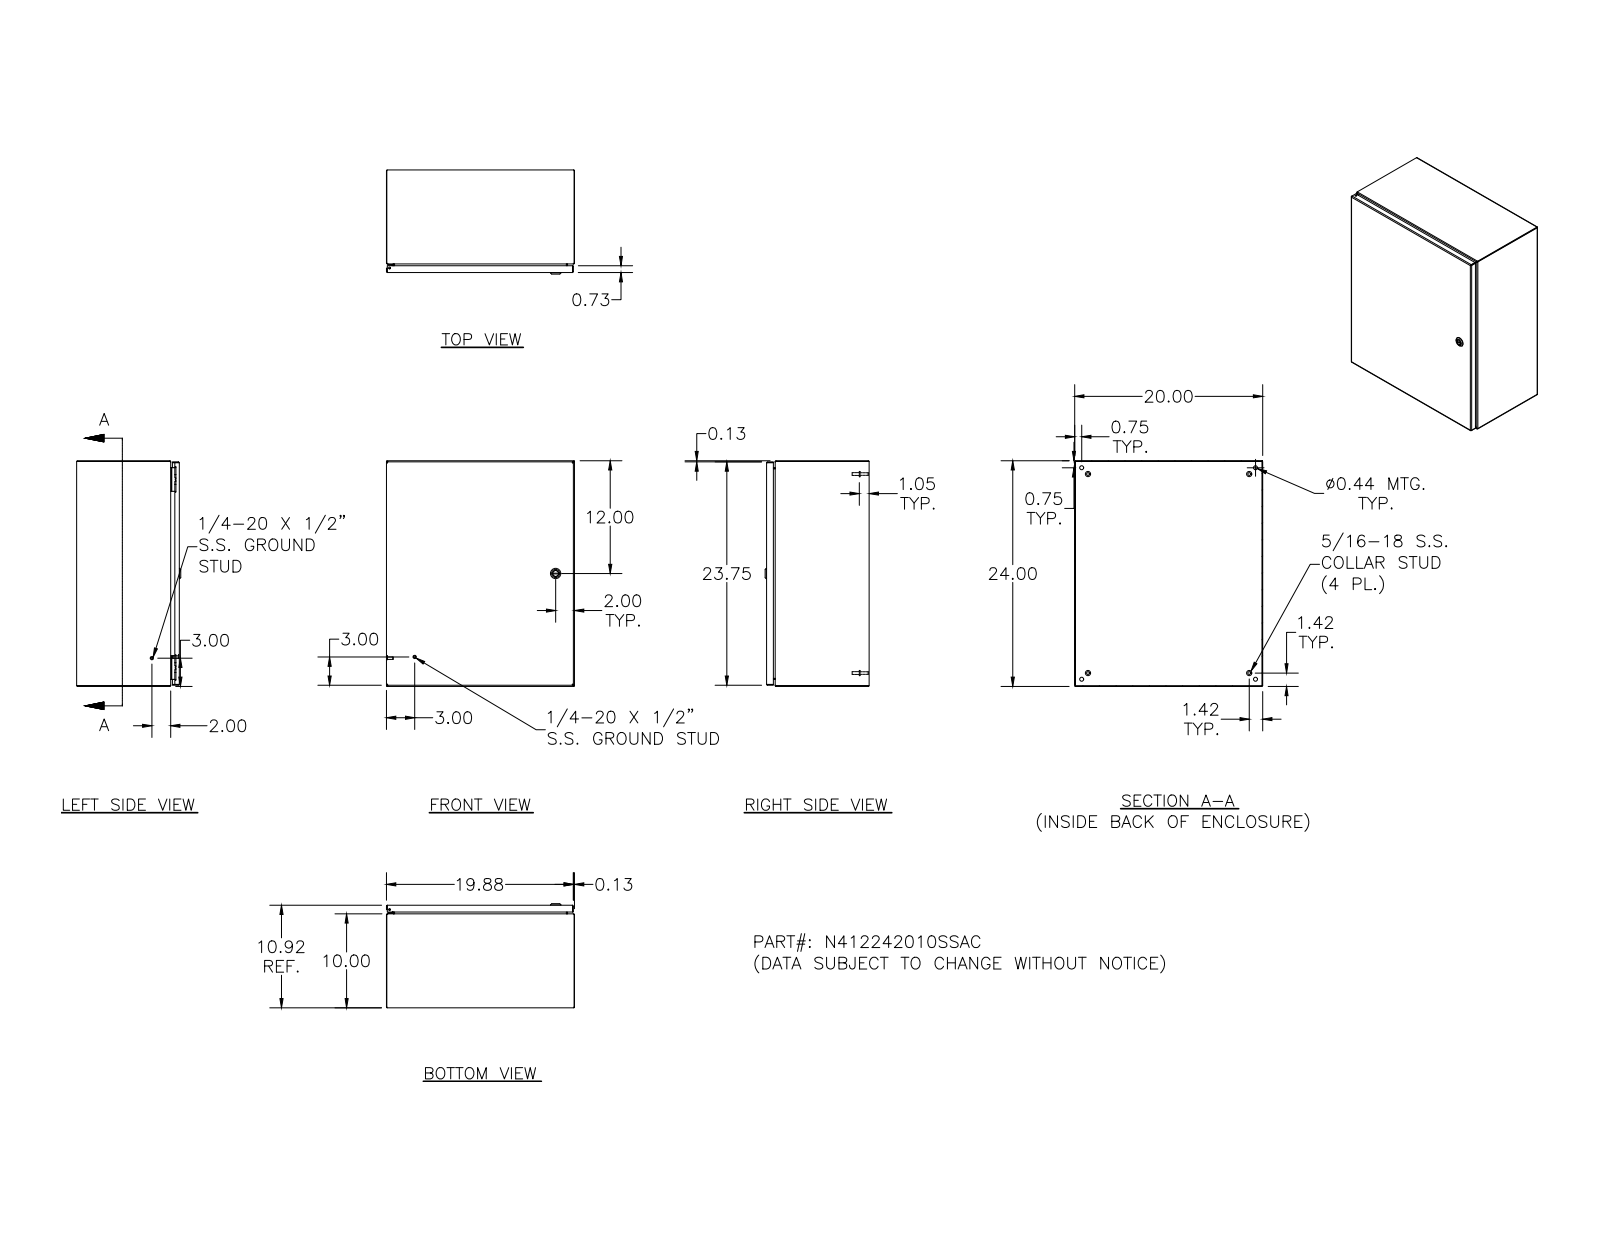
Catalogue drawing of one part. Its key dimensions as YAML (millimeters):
part_name: "N412242010SSAC; N412242010SSACBKP; 388151; N4122420SSACLID (+8 more)"
step_written_by: "Autodesk Inventor 2011 (AUTOMOTIVE_DESIGN)"
units: millimeters
bodies: {solids: 34, faces: 1364, planar: 523, cylindrical: 497, other: 344}
overall_size: [609.6, 508, 281.3]
volume: 2447000
surface_area: 2617000
round_holes:
  - {diameter: 4.8, count: 5}
  - {diameter: 2.4, count: 4}
  - {diameter: 3.9, count: 4}
  - {diameter: 4.2, count: 4}
  - {diameter: 4.4, count: 4}
  - {diameter: 11.1, count: 4}
  - {diameter: 4, count: 2}
  - {diameter: 4.7, count: 1}
  - {diameter: 5, count: 1}
  - {diameter: 8, count: 1}
  - {diameter: 10, count: 1}
  - {diameter: 10.2, count: 1}
round_bosses_or_shafts:
  - {diameter: 6.4, count: 10}
  - {diameter: 14.3, count: 4}
  - {diameter: 9.1, count: 4}
  - {diameter: 8.1, count: 4}
  - {diameter: 7.6, count: 4}
  - {diameter: 7, count: 4}
  - {diameter: 6.5, count: 4}
  - {diameter: 4.2, count: 4}
partial_cylinders:
  - {radius: 1.3, count: 26}
  - {radius: 0.4, count: 18}
  - {radius: 0.4, count: 16}
  - {radius: 2.3, count: 16}
  - {radius: 0.8, count: 14}
  - {radius: 3.2, count: 14}
  - {radius: 0.5, count: 9}
  - {radius: 0.8, count: 8}
face_to_face_distances: [1.9, 275.4, 506.1, 273.5, 277.3, 607.7, 508, 504.2, 609.6, 605.8]
hole_center_spacings: [508, 0.4, 16.8, 479.3, 0.5, 12.7, 16.5, 16.6]
